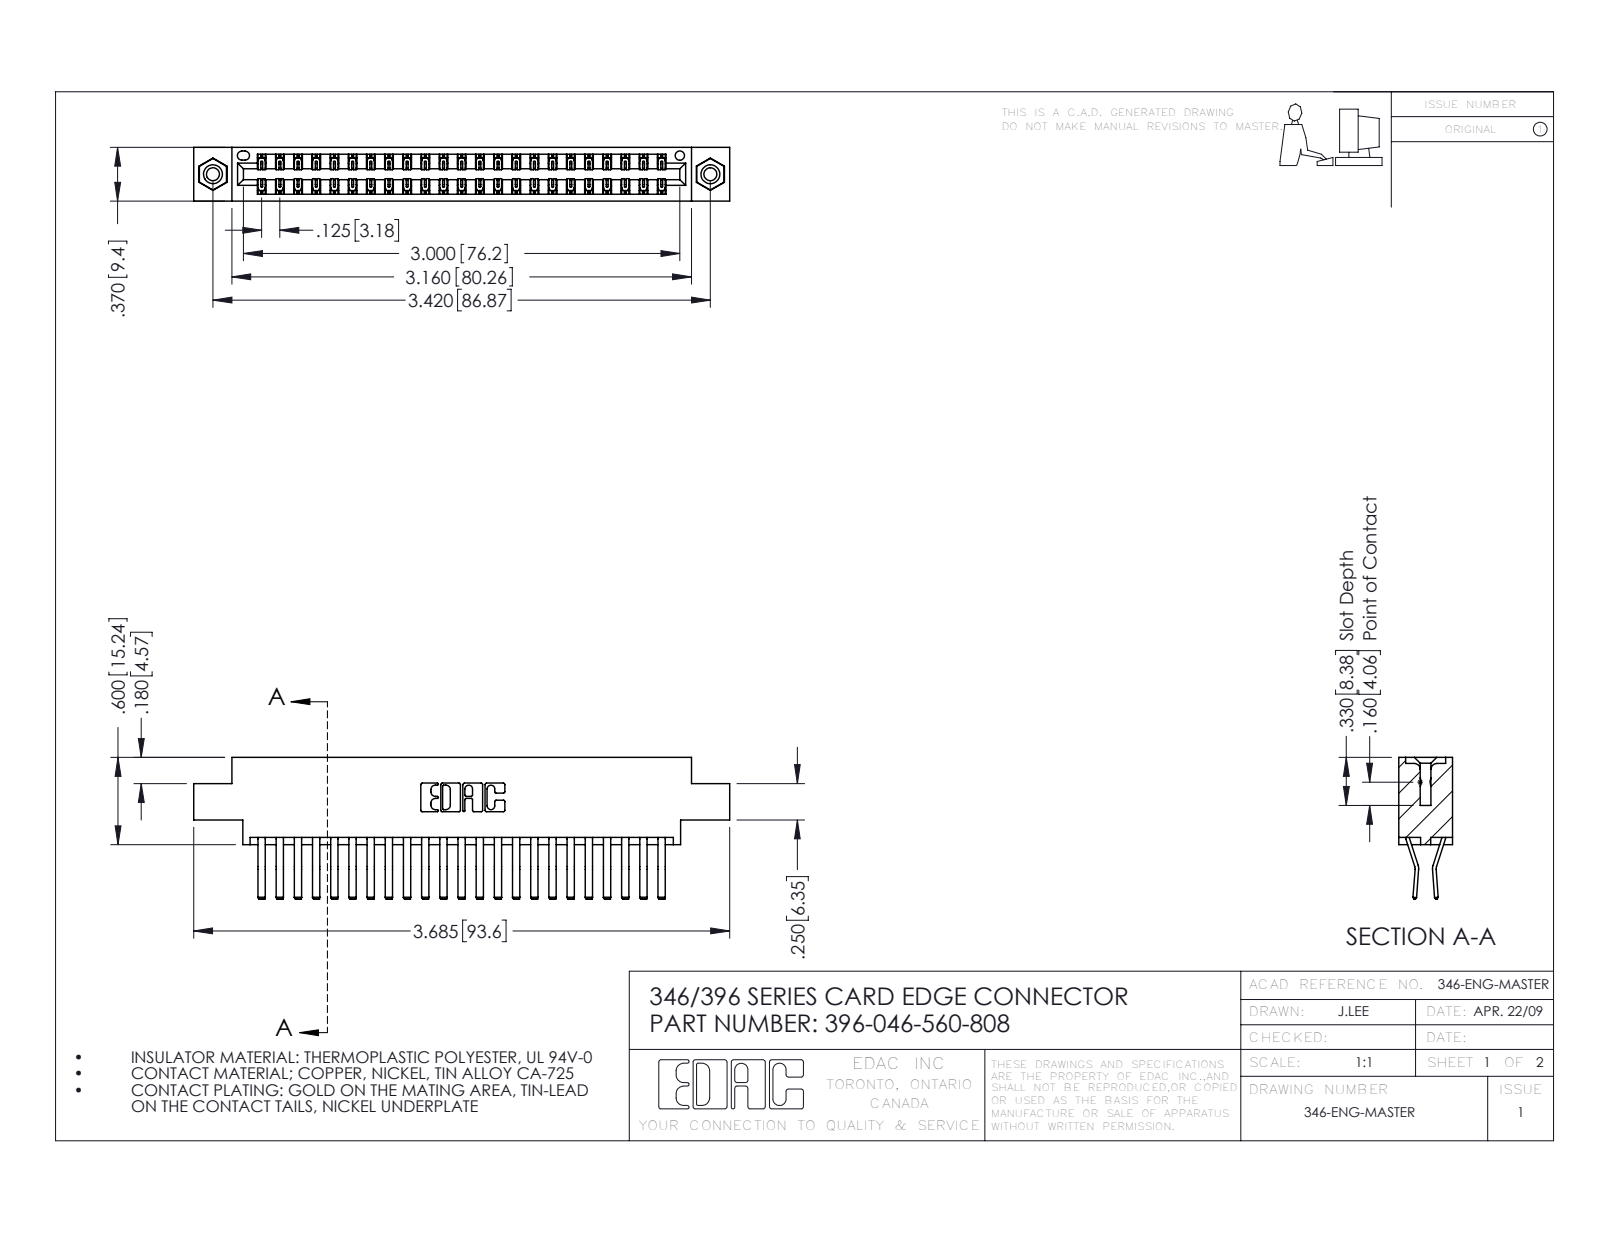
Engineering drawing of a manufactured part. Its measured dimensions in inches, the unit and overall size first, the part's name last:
Units: inches
Overall size (bounding box): 3.685 × 0.975 × 0.37
Round holes (diameter × count): ⌀0.089 ×2, ⌀0.125 ×2, ⌀0.156 ×2, ⌀0.064 ×1
Round bosses / shafts (diameter × count): ⌀0.155 ×2
Partial cylindrical surfaces — rounded edges, fillets, slot ends (radius × count): R0.006 ×69, R0.01 ×22, R0.007 ×6, R0.031 ×6, R0.026 ×3, R0.01 ×2, R0.014 ×2, R0.022 ×2
Main face-to-face distances: 0.048, 0.322, 0.37, 0.25, 0.025, 0.072, 0.298, 0.275, 0.222, 0.148
Hole centre spacings: 0.246, 3.212, 3.42
Volume: 0.557 in³ · Surface area: 20.52 in²
Bodies: 49 solids, 2670 faces (1722 planar, 932 cylindrical, 16 other)
Part name (STEP PRODUCT): 396-046-560-808; 345-250-001_345-250-003-102; 346 Part_0.170 Offset - 0.156 Dia-TI; 345-292-001_560 Tail
STEP written by: SolidWorks 2016 (CONFIG_CONTROL_DESIGN)
